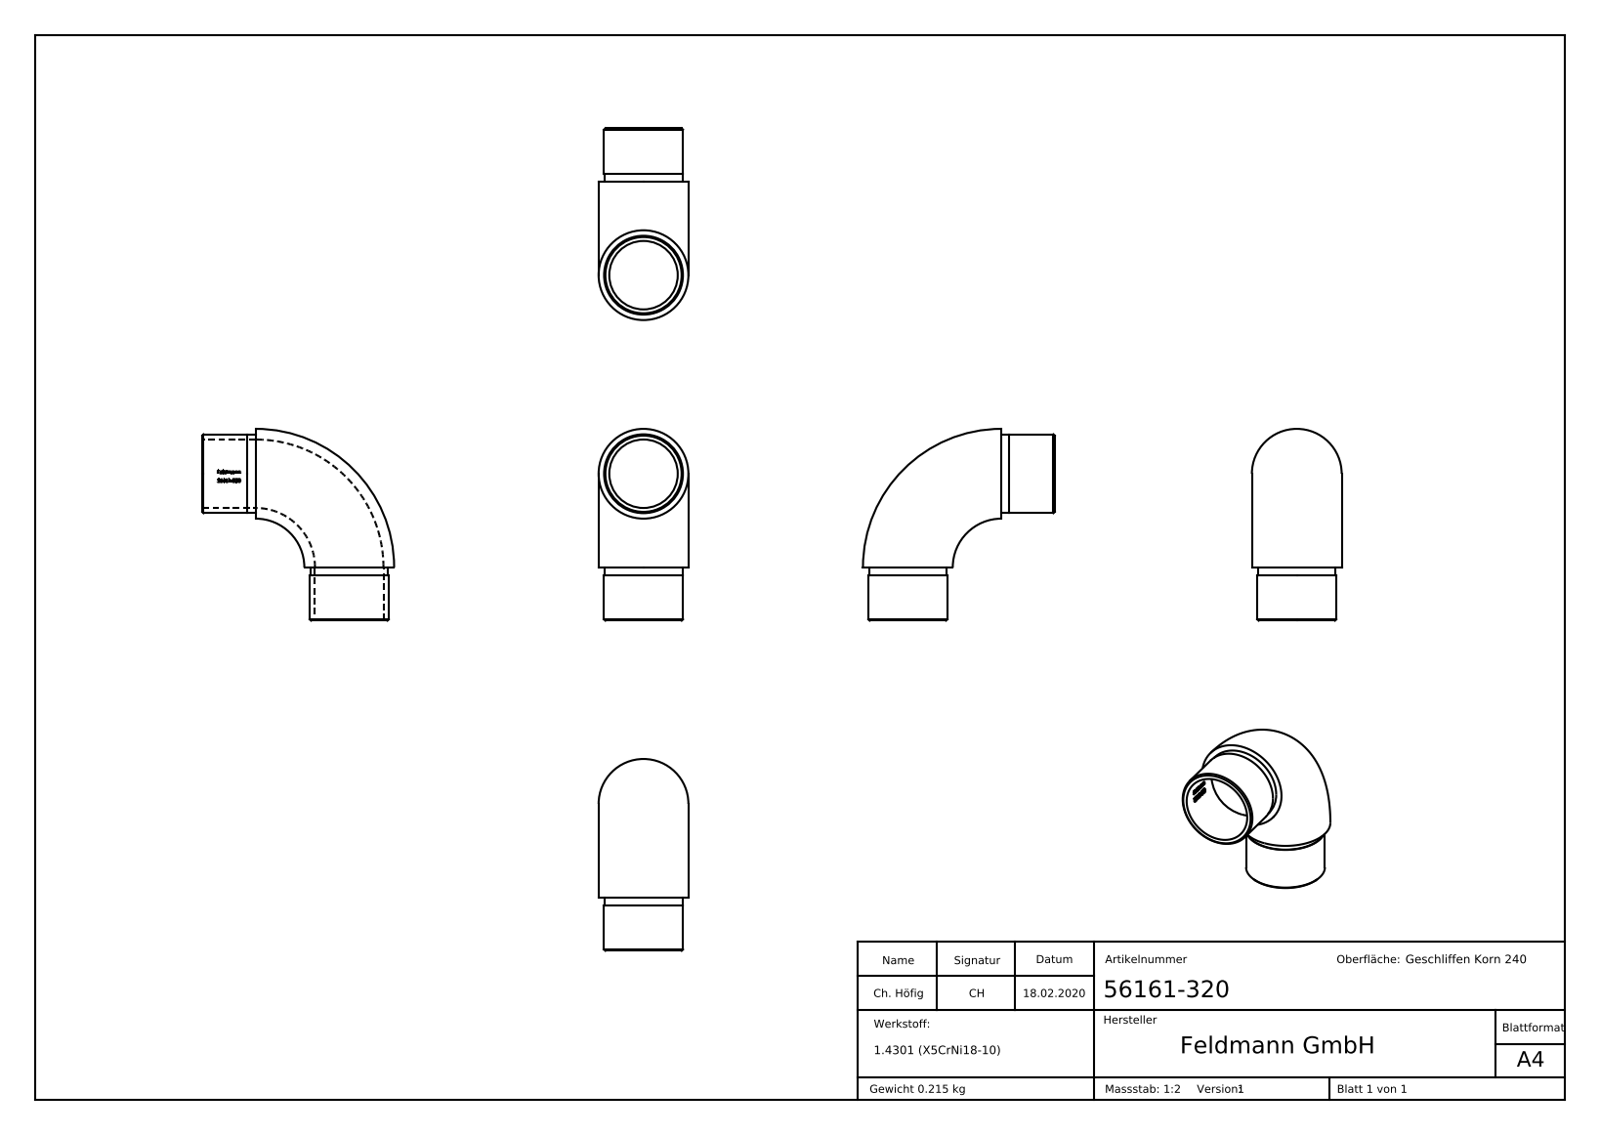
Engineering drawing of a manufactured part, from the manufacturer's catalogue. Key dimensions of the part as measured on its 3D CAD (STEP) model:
Part name (STEP PRODUCT): 56161-320
STEP written by: SolidWorks 2015 (CONFIG_CONTROL_DESIGN)
Units: millimetres
Bodies: 1 solid, 233 faces (97 planar, 29 cylindrical, 107 other)
Overall size (bounding box): 72 × 72 × 33.7
Volume: 27 248 mm³ · Surface area: 18 020 mm²
Round holes (diameter × count): ⌀25.7 ×2
Round bosses / shafts (diameter × count): ⌀29.6 ×2, ⌀29.2 ×2
Partial cylindrical surfaces — rounded edges, fillets, slot ends (radius × count): R12.95 ×1
Main face-to-face distances: 20, 17, 3, 0.39, 1.26, 3.2, 4.23, 2.03, 4.43, 2.97
